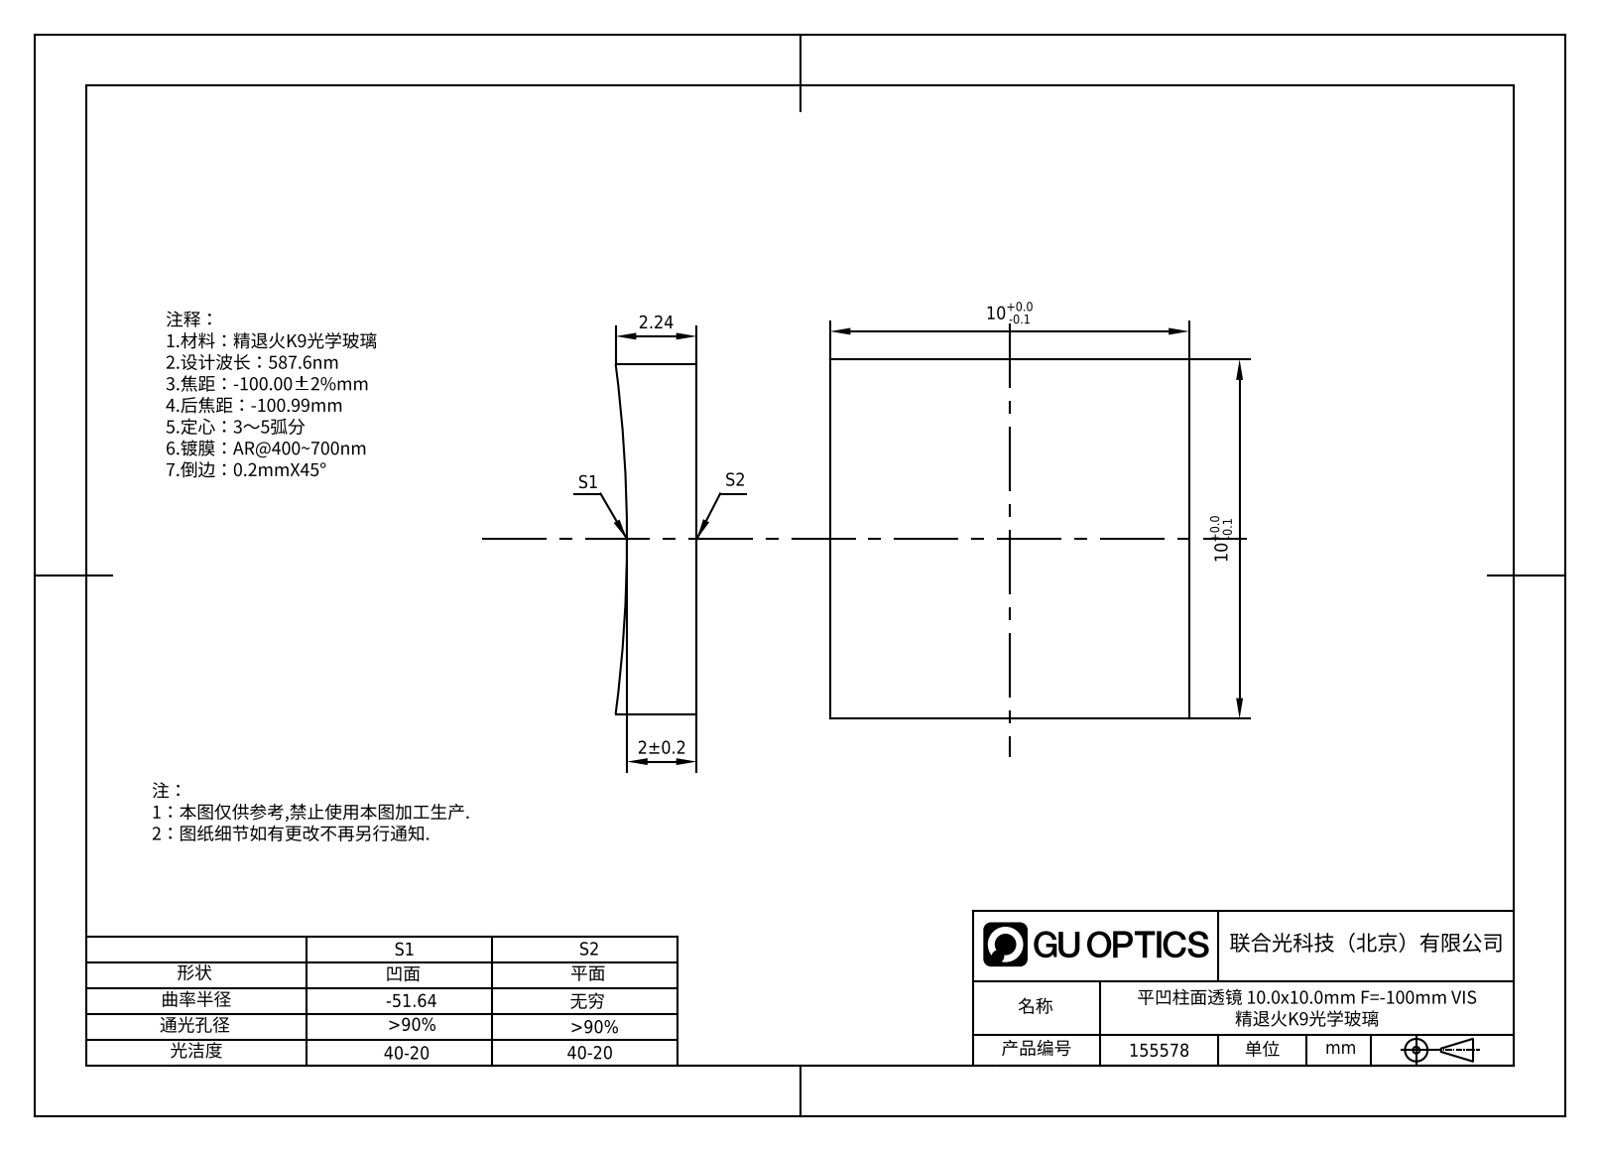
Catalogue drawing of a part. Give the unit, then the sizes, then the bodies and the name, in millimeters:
Units: millimetres
Overall size (bounding box): 10 × 10 × 2.24
Partial cylindrical surfaces — rounded edges, fillets, slot ends (radius × count): R51.64 ×1
Main face-to-face distances: 10
Volume: 208 mm³ · Surface area: 287 mm²
Bodies: 1 solid, 6 faces (5 planar, 1 cylindrical, 0 other)
Part name (STEP PRODUCT): 155568
STEP written by: SolidWorks 2020 (CONFIG_CONTROL_DESIGN)
